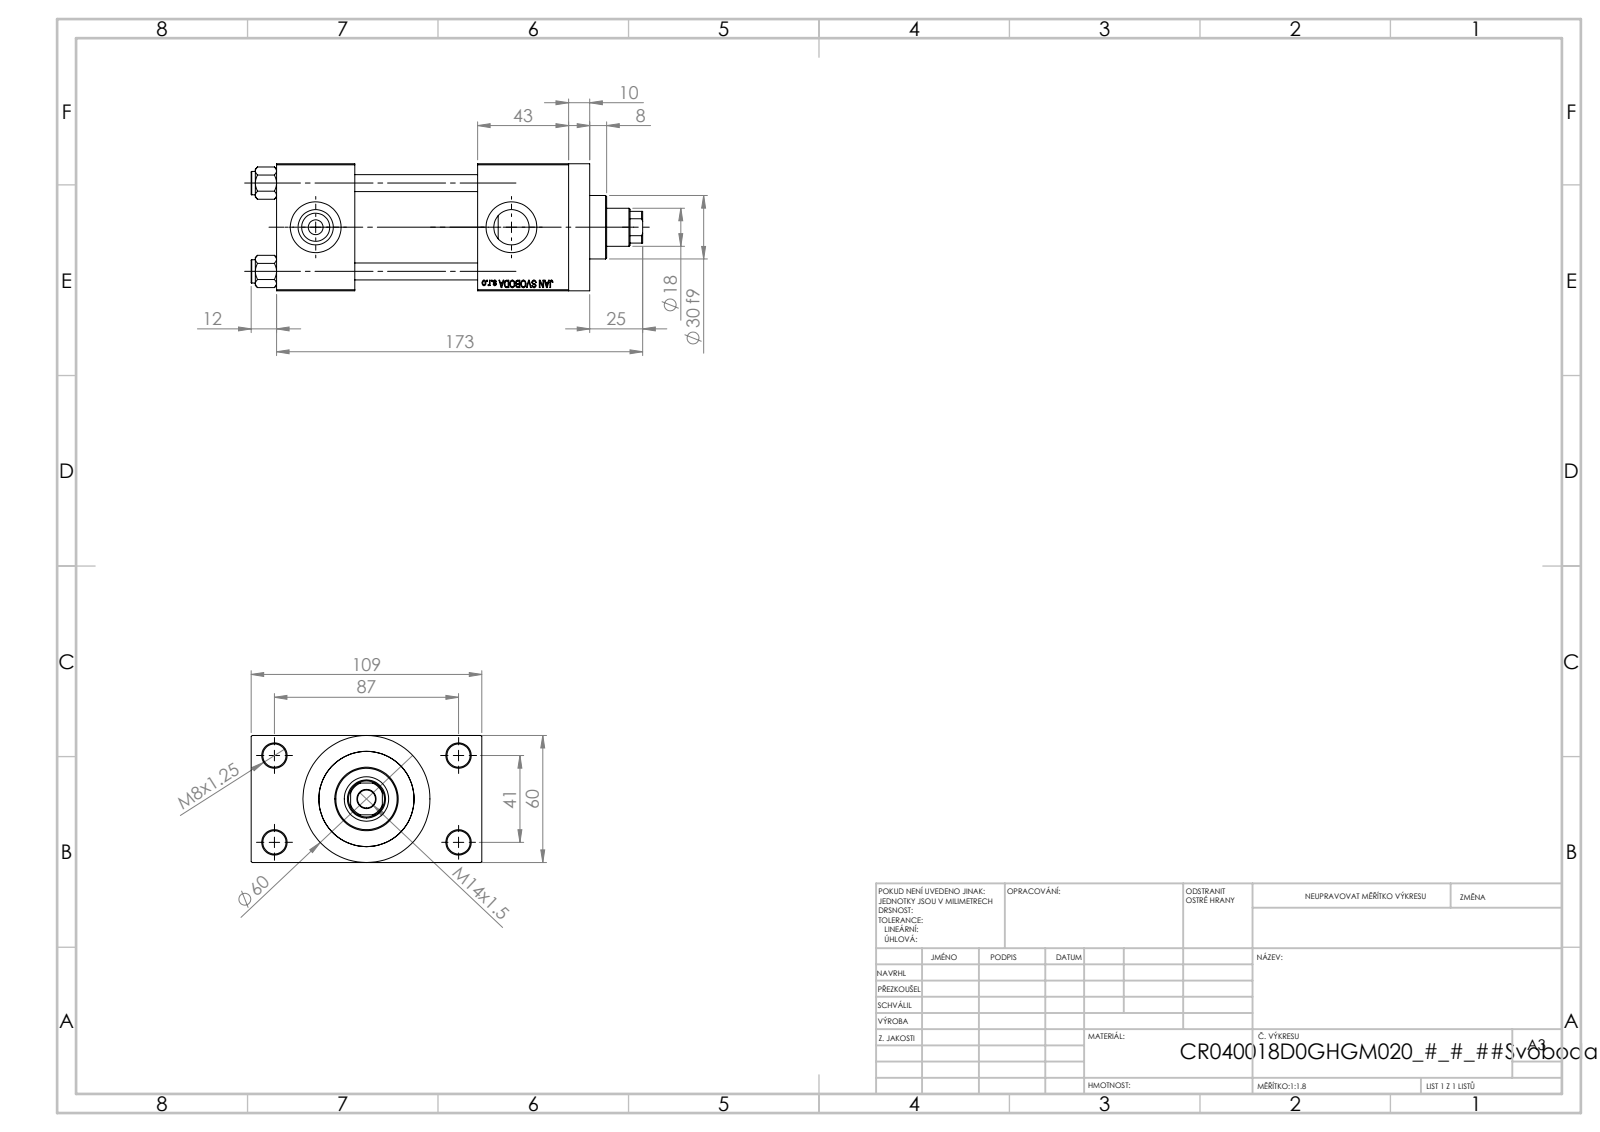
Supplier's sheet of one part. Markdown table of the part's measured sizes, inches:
| quantity | value |
| --- | --- |
| part name | NUT_M5_D; V215_VC_A; V215CR_VCP_D; V215CR_D_TYCINKA (+1 more) |
| STEP written by | SolidWorks 2019 (CONFIG_CONTROL_DESIGN) |
| units | inches |
| bodies | 11 solids, 1104 faces (498 planar, 88 cylindrical, 518 other) |
| overall size | 7.283 × 4.291 × 2.362 |
| volume | 31.28 in³ |
| surface area | 189.9 in² |
| round holes (diameter × count) | 0.315 × 4, 0.433 × 4, 0.276 × 2, 0.656 × 2, 0.945 × 2, 0.335 × 1, 0.709 × 1, 0.827 × 1, 1.22 × 1, 1.575 × 1, 1.772 × 1 |
| round bosses / shafts (diameter × count) | 0.433 × 4, 2.362 × 1, 1.811 × 1, 1.181 × 1 |
| partial cylindrical surfaces (radius × count) | 0.335 × 1 |
| main face-to-face distances | 2.362, 2.283, 0.965, 3.327, 1.457, 3.74, 5.433, 3.976, 1.693, 0.394 |
| hole center spacings | 0.892, 1.161, 1.642, 1.856, 1.893, 2.533, 3.011, 1.614 |
